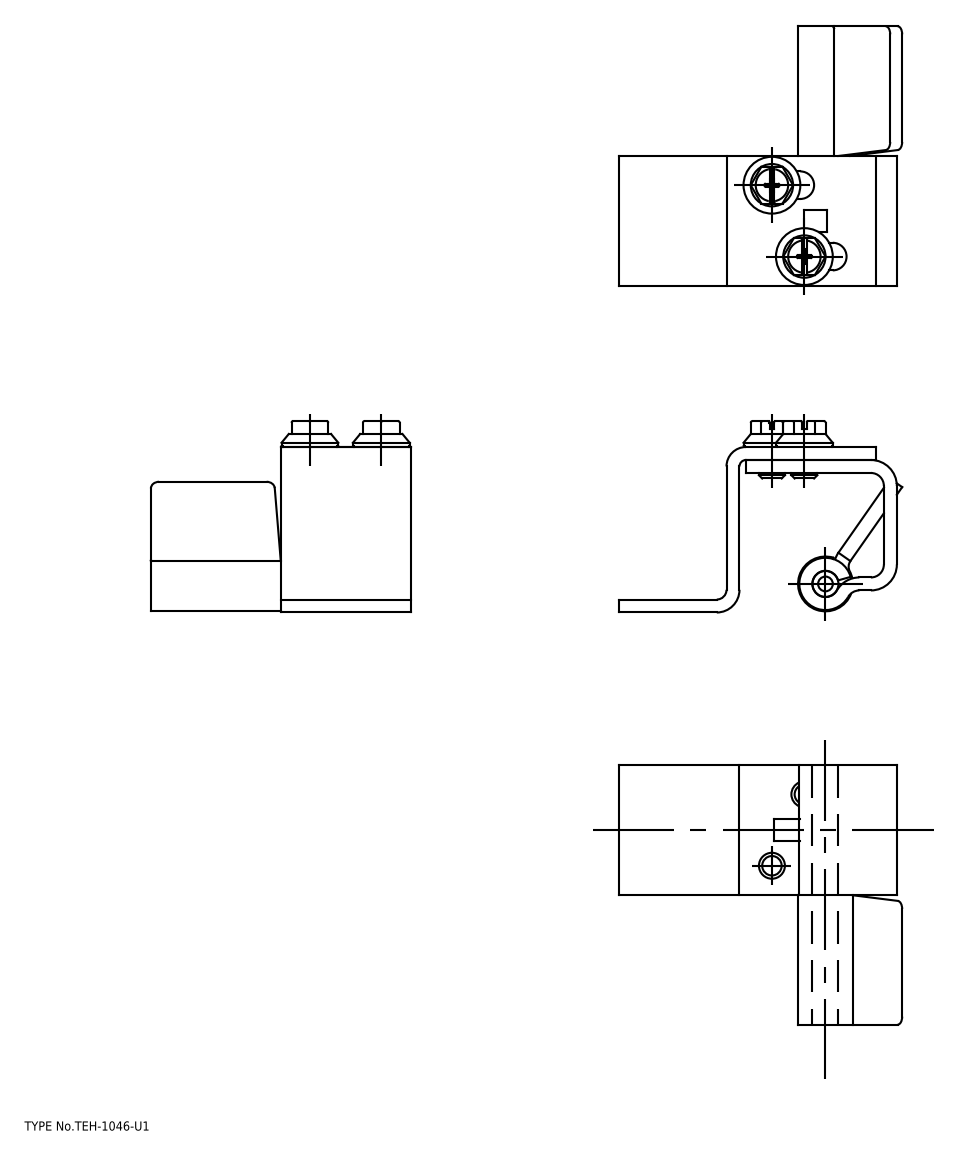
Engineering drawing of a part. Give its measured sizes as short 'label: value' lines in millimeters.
name: PC010-prt0; PC010-prt1; 1046-U1_asm_M2; 1046-U1_asm_M3 (+4 more)
written by: spGate 17.5.2 (AUTOMOTIVE_DESIGN)
unit: mm
bodies: 6 solids, 303 faces (121 planar, 134 cylindrical, 48 other)
size: 87.14 × 80 × 58.85
volume: 56 563 mm³; area: 32 771 mm²
holes: 2× ⌀7, 2× ⌀10, 1× ⌀8, 1× ⌀8.05, 1× ⌀8.1
bosses: 2× ⌀17.5, 2× ⌀8, 1× ⌀16.9, 1× ⌀16.1
rounds: 68× R0.3, 8× R0.5, 4× R4.25, 3× R4, 3× R8, 2× R2.5, 2× R3, 1× R2
face distances: 4, 47, 43, 48.5, 40, 39, 8, 51, 4.52, 44.5
hole spacings: 24.17
